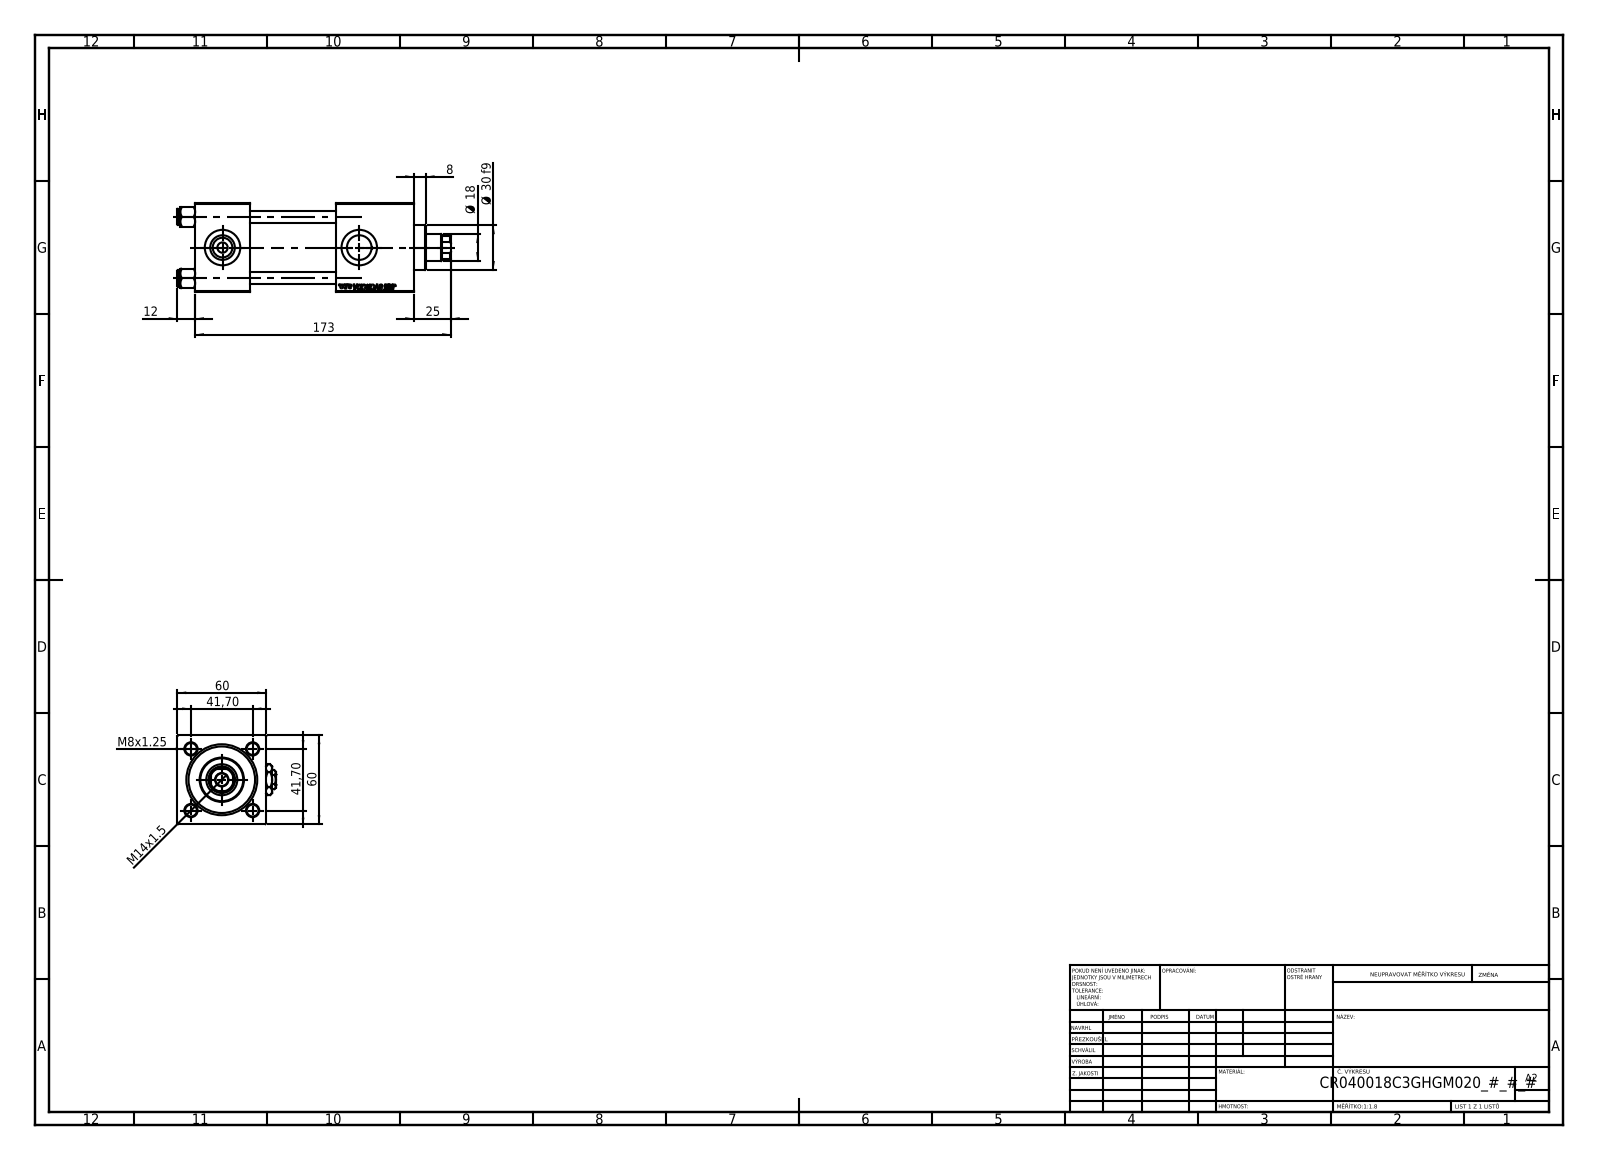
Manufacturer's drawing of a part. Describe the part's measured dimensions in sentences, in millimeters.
The part is named "NUT_M5_C; V215CR_C_Body; V215CR_VCP_C; V215_VC_A (+2 more)". Its 3-D file was written by "SolidWorks 2019 (CONFIG_CONTROL_DESIGN)". It is 13 solids with 1250 faces: 574 planar, 98 cylindrical and 578 other. Overall it measures 185 by 67 by 60 millimeters. Its volume is 399 322 cubic millimeters and its surface area 108 248 square millimeters. Round holes: 4 of diameter 8, 2 of diameter 7, 2 of diameter 16.66, 2 of diameter 24, 1 of diameter 8.5, 1 of diameter 18, 1 of diameter 21, 1 of diameter 31, 1 of diameter 40, 1 of diameter 45. Round bosses or shafts: 4 of diameter 11, 1 of diameter 46, 1 of diameter 30. Partial cylindrical surfaces (rounded edges, fillets, slot ends): 1 of radius 8.5. The main face-to-face distances are 60, 37, 53, 148, 111, 58, 95, 119.3, 82.3, 24.3. The hole center spacings are 29.49, 41.7, 58.97, 92.5.
